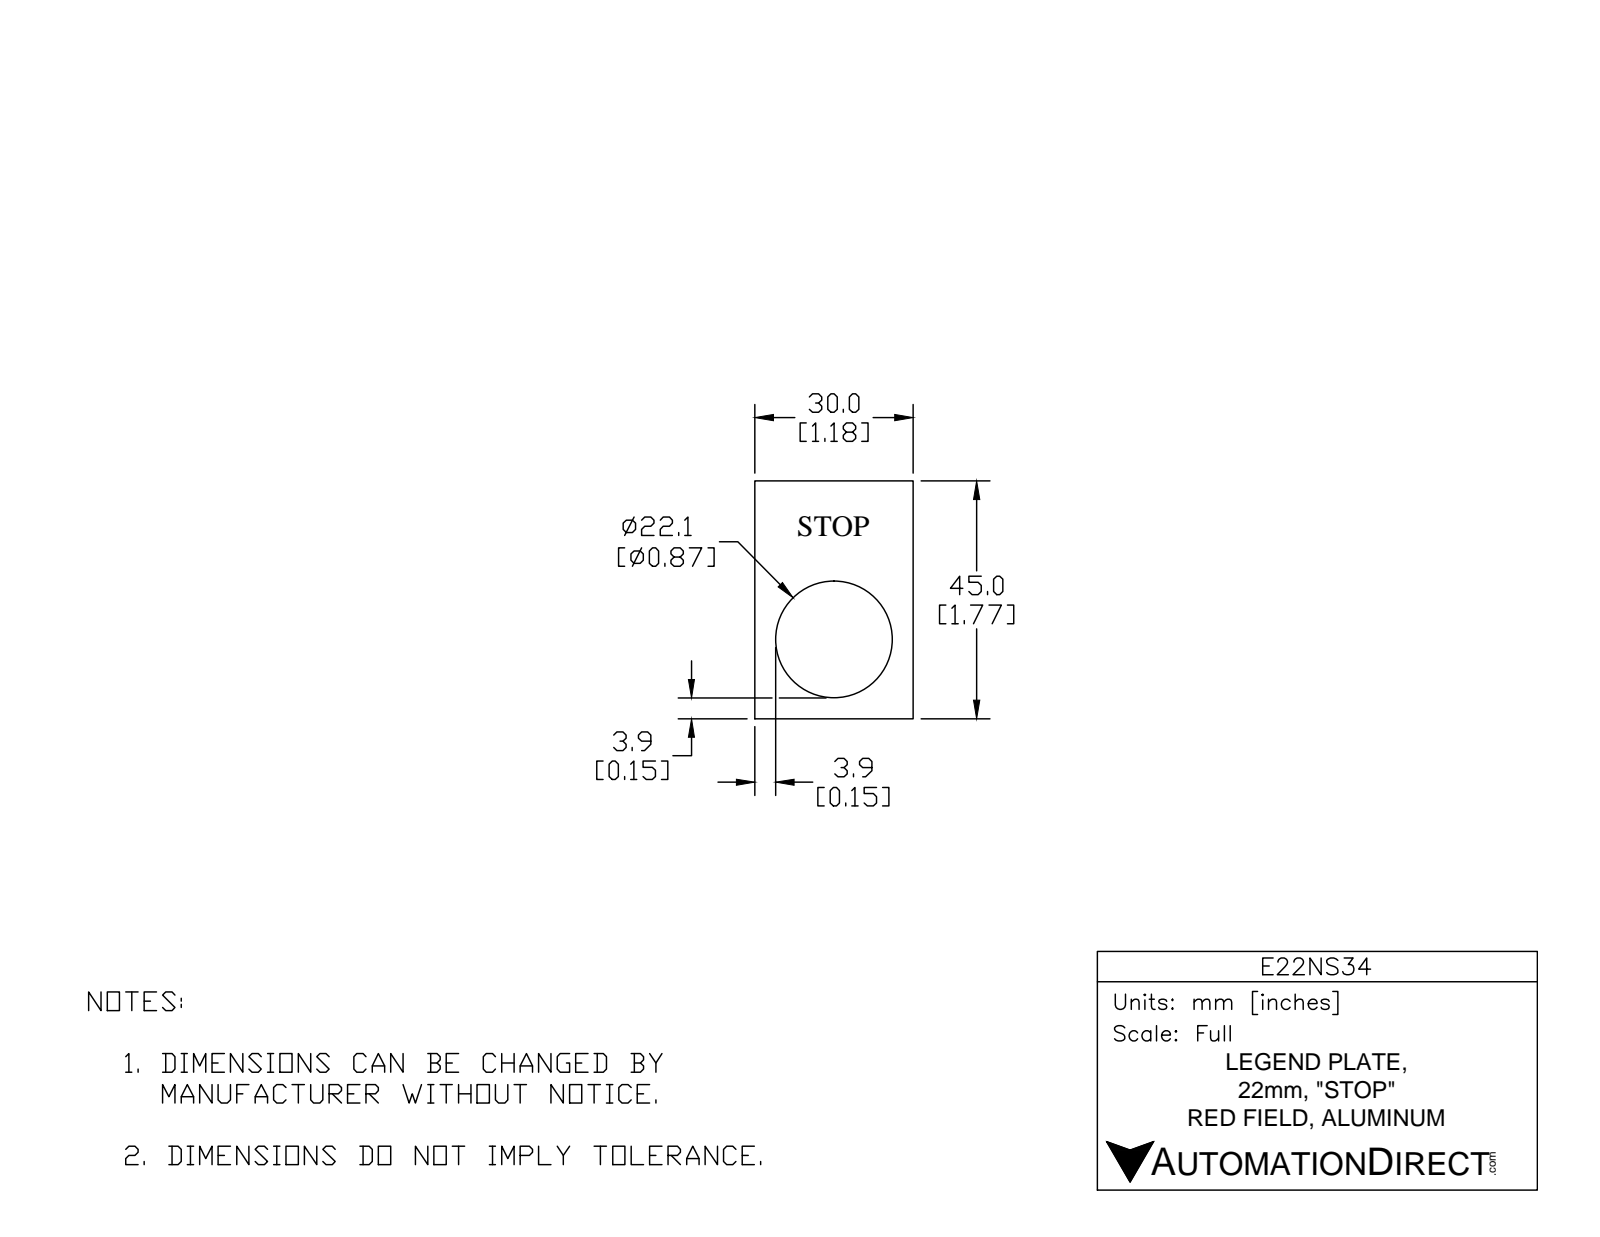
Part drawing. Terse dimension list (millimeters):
name: E22NS34
written by: SolidWorks 2017 (AUTOMOTIVE_DESIGN)
unit: mm
bodies: 1 solid, 65 faces (33 planar, 3 cylindrical, 29 other)
size: 45 × 30 × 1.3
volume: 1 252 mm³; area: 2 236 mm²
holes: 1× ⌀22.2
face distances: 1.3, 30, 45, 1.05, 4.7, 40.3, 13.4, 16.6, 0.36, 6.66
